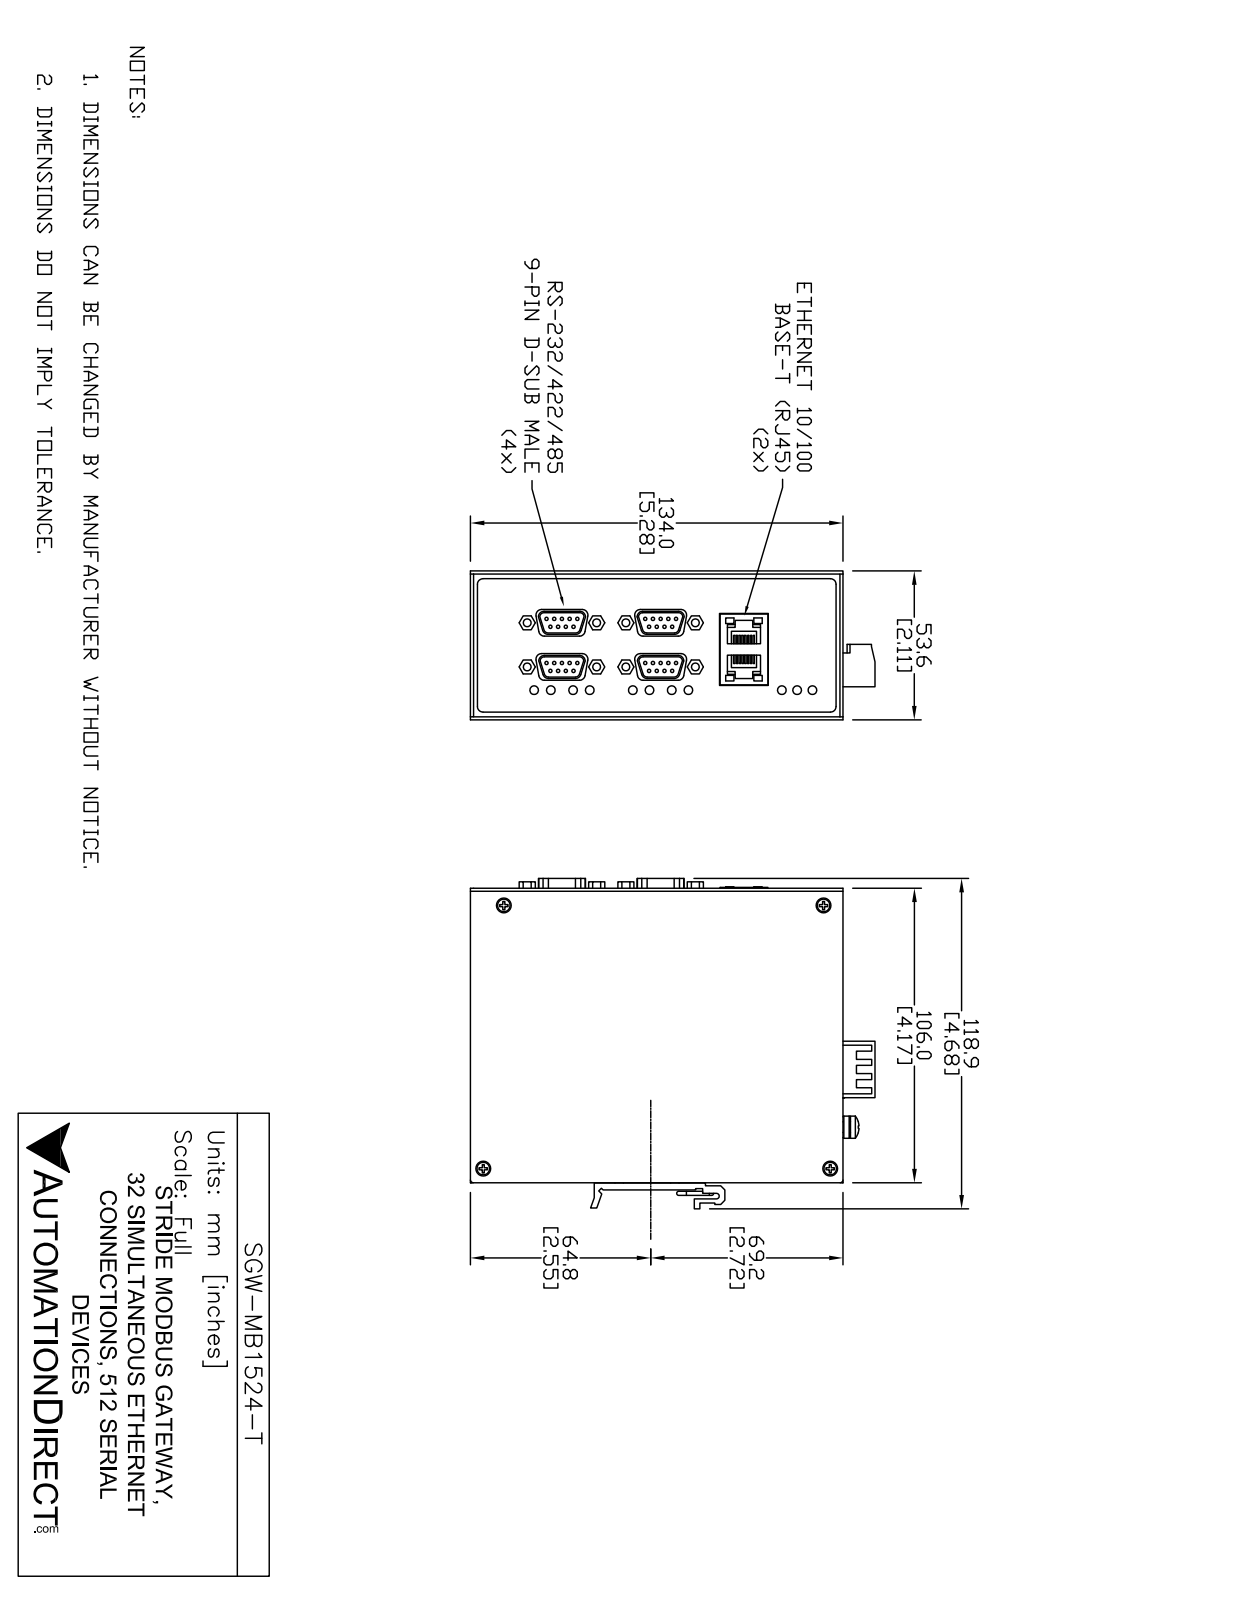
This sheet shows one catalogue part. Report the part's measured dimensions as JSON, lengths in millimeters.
{"part_name": "SGW-MB1524-T", "step_written_by": "SolidWorks 2017 (AUTOMOTIVE_DESIGN)", "units": "millimeters", "bodies": {"solids": 0, "faces": 1789, "planar": 962, "cylindrical": 553, "other": 274}, "overall_size": [145.5, 118.9, 53.6], "round_holes": [[2.5, 8], [2.8, 8], [3.8, 4], [3, 3], [3.5, 2], [2, 1]], "round_bosses_or_shafts": [[1.2, 36], [3.5, 20], [3.1, 11], [6.3, 9], [4.5, 7], [2.8, 7], [2.4, 7], [1.5, 6]], "partial_cylinders_radius": [[2, 40], [1.5, 16], [1, 15], [0.1, 8], [0.5, 8], [3, 8], [1.1, 6], [1.5, 6]], "face_to_face_distances": [1, 51.6, 52.6, 2, 0.5, 50.6, 53.6, 104.5, 52.1, 51.1], "hole_center_spacings": [15.9, 25, 29.6, 35.5, 38.9, 150.8, 5.2, 10.2]}
